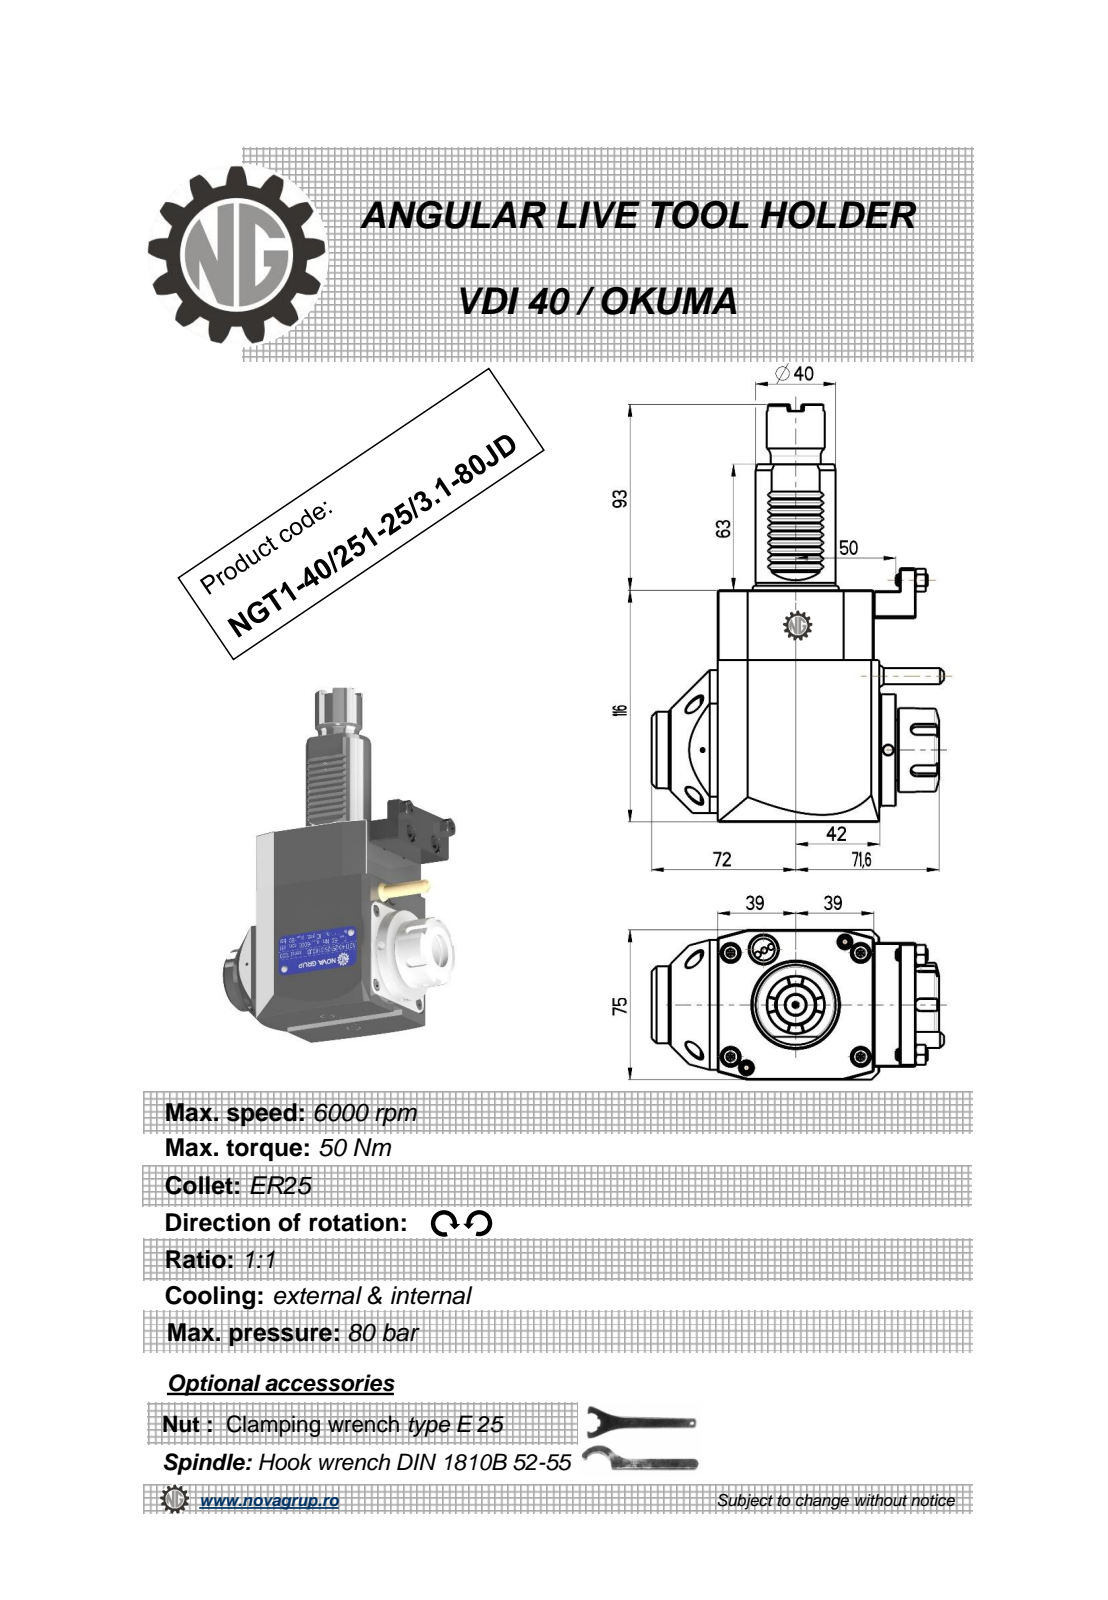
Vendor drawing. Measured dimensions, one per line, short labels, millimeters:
name: NGT1_40_251_25_3_1_80JD
written by: PRO/ENGINEER BY PARAMETRIC TECHNOLOGY CORPORATION, 2010280 (CONFIG_CONTROL_DESIGN)
unit: mm
bodies: 1 solid, 468 faces (189 planar, 83 cylindrical, 196 other)
size: 209 × 146.14 × 75
volume: 926 366 mm³; area: 76 385 mm²
holes: 3× ⌀5, 1× ⌀3, 1× ⌀20.3
bosses: 2× ⌀6, 1× ⌀56, 1× ⌀43, 1× ⌀42, 1× ⌀40, 1× ⌀38.5, 1× ⌀33, 1× ⌀29
rounds: 10× R0.3, 10× R0.31, 6× R0.2, 5× R3, 1× R0.5, 1× R10, 1× R40
face distances: 75, 116, 10, 0.5, 81, 11, 8, 21, 80.8, 3
hole spacings: 40.93
